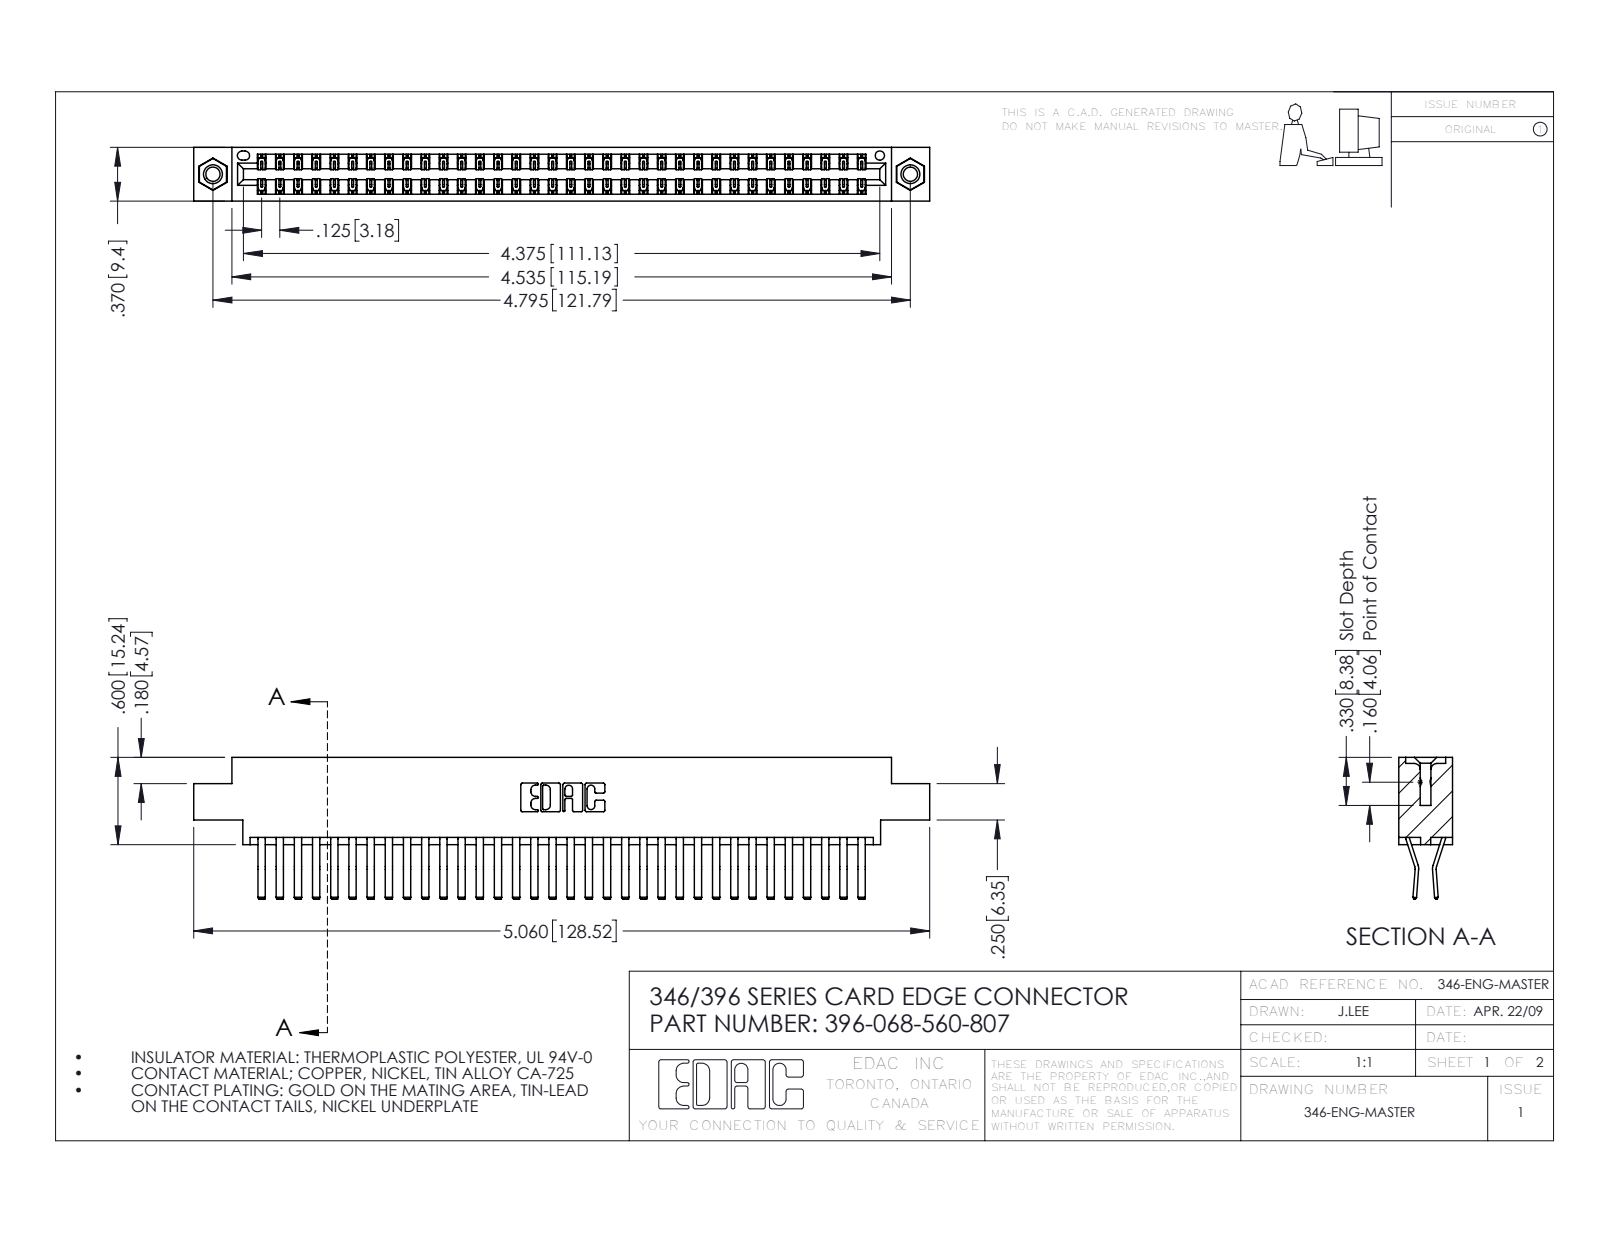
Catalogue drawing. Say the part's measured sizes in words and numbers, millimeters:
The part is named "396-068-560-807; 345-250-001_345-250-005-103; 345-292-001_560 Tail; 346 Part_0.170 Offset - 0.156 Dia-TI". Its 3-D file was written by "SolidWorks 2016 (CONFIG_CONTROL_DESIGN)". It is 71 solids with 3858 faces: 2492 planar, 1350 cylindrical and 16 other. Overall it measures 128.5 by 24.8 by 9.4 millimeters. Its volume is 12 700 cubic millimeters and its surface area 18 800 square millimeters. Round holes: 2 of diameter 2.5, 2 of diameter 3.2, 2 of diameter 4, 1 of diameter 1.6. Round bosses or shafts: 2 of diameter 3.9. Partial cylindrical surfaces (rounded edges, fillets, slot ends): 102 of radius 0.2, 22 of radius 0.3, 6 of radius 0.2, 6 of radius 0.8, 3 of radius 0.7, 2 of radius 0.3, 2 of radius 0.4, 2 of radius 0.6. The main face-to-face distances are 1.2, 8.2, 9.4, 0.6, 6.4, 1.8, 7.6, 7, 5.6, 3.8. The hole center spacings are 6.2, 116.5, 121.8.
